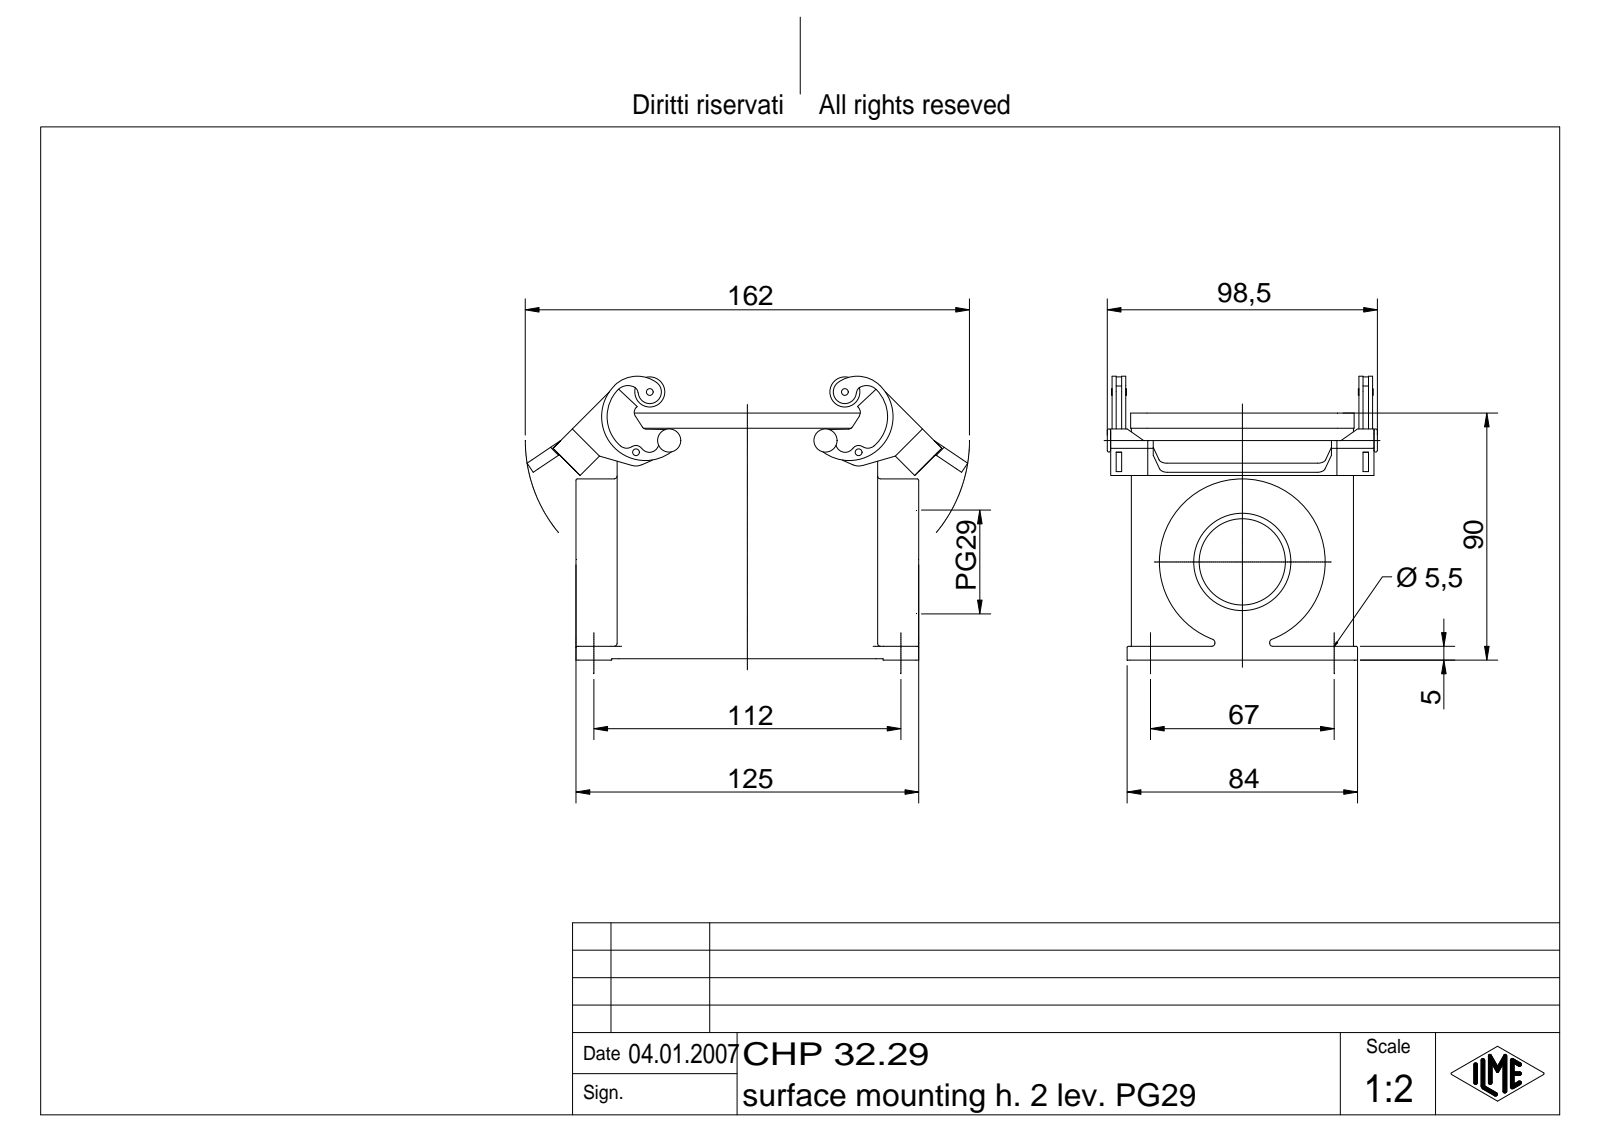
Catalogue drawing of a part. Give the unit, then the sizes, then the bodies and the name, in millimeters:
Units: millimetres
Overall size (bounding box): 160.7 × 103.44 × 98.5
Round holes (diameter × count): ⌀2 ×4, ⌀2.46 ×4, ⌀3.1 ×4, ⌀2.5 ×2, ⌀5.5 ×2, ⌀31.48 ×1, ⌀35.48 ×1
Round bosses / shafts (diameter × count): ⌀11 ×2, ⌀5 ×2, ⌀3 ×2, ⌀60.5 ×1
Partial cylindrical surfaces — rounded edges, fillets, slot ends (radius × count): R1 ×23, R0.5 ×14, R1.5 ×8, R3 ×8, R6 ×8, R2.5 ×6, R2 ×4, R3.5 ×4
Main face-to-face distances: 3, 78, 81, 4.5, 75, 4, 92, 90, 3.25, 95
Hole centre spacings: 22.56, 27, 77.5, 79.27, 82.07, 17.37, 33.74, 41.73
Volume: 272 788 mm³ · Surface area: 108 719 mm²
Bodies: 1 solid, 818 faces (156 planar, 269 cylindrical, 393 other)
Part name (STEP PRODUCT): CHP 32.29
STEP written by: Autodesk Inventor 7 (AUTOMOTIVE_DESIGN)
